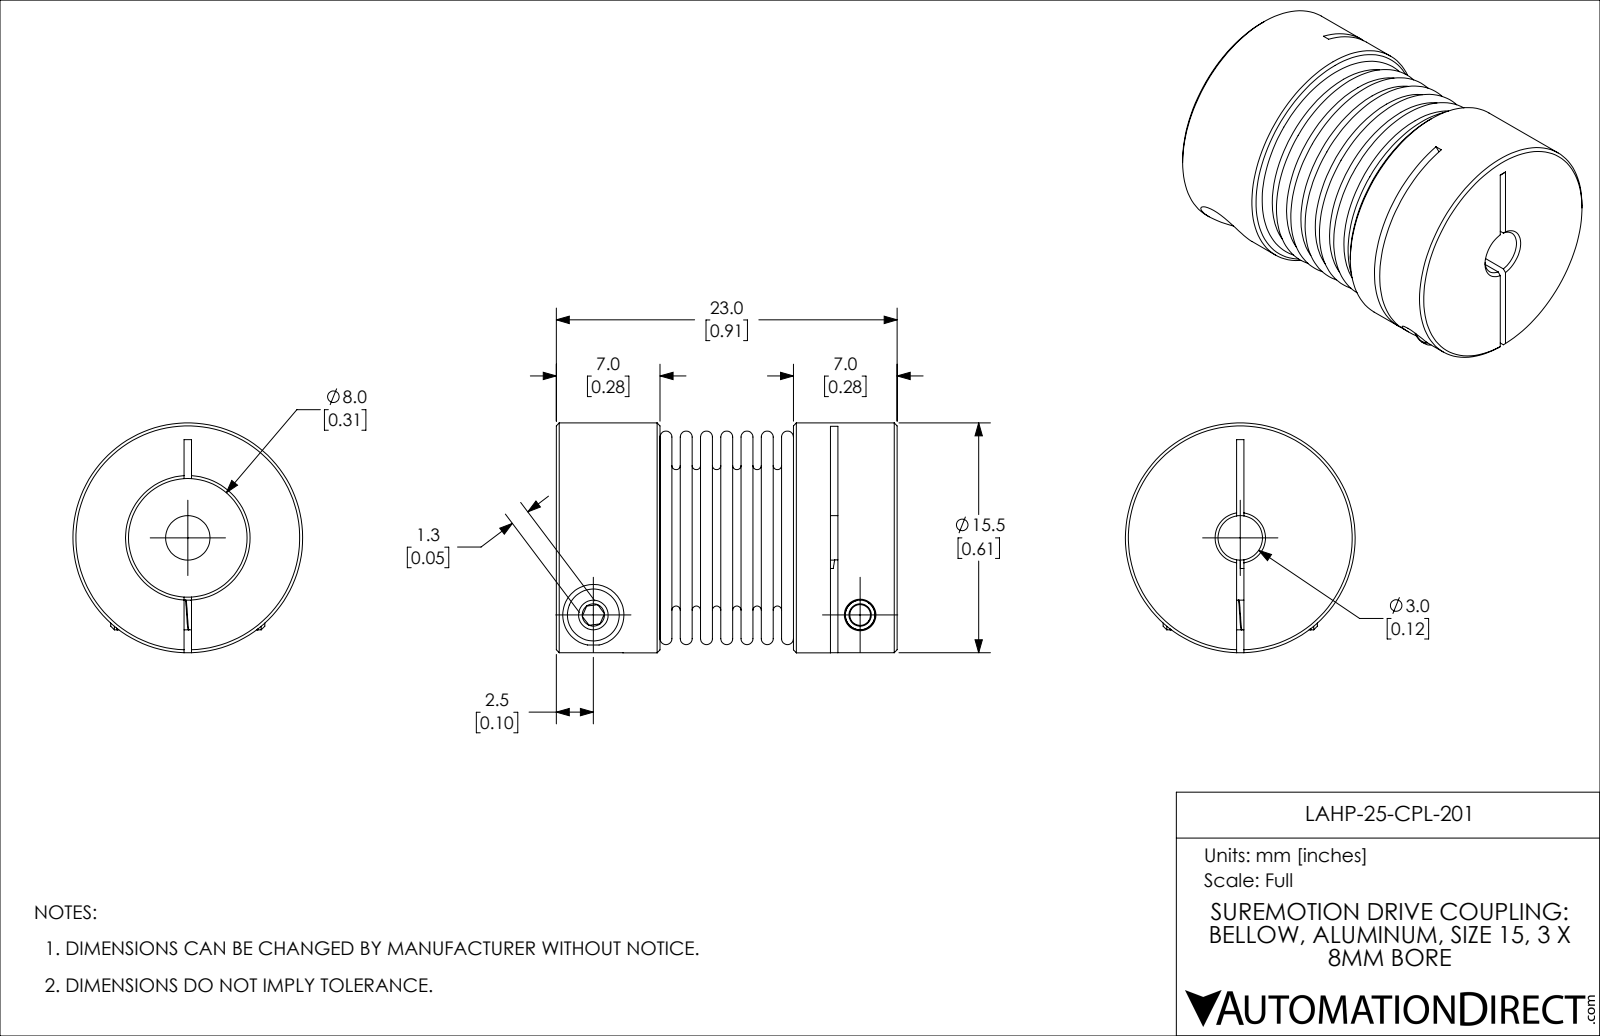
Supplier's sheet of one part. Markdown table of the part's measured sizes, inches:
| quantity | value |
| --- | --- |
| part name | LAHP-25-CPL-201 |
| STEP written by | SolidWorks 2019 (CONFIG_CONTROL_DESIGN) |
| units | inches |
| bodies | 5 solids, 401 faces (66 planar, 197 cylindrical, 138 other) |
| overall size | 0.906 × 0.61 × 0.61 |
| volume | 0.141 in³ |
| surface area | 7.9 in² |
| round holes (diameter × count) | 0.084 × 2, 0.162 × 2, 0.118 × 1, 0.315 × 1, 0.384 × 1 |
| round bosses / shafts (diameter × count) | 0.138 × 2, 0.079 × 2, 0.058 × 2, 0.61 × 1 |
| partial cylindrical surfaces (radius × count) | 0.63 × 4 |
| main face-to-face distances | 0.161, 0.054, 0.107, 0.08, 0.081, 0.026, 0.215, 0.054, 0.028, 0.135 |
| hole center spacings | 0.709 |
